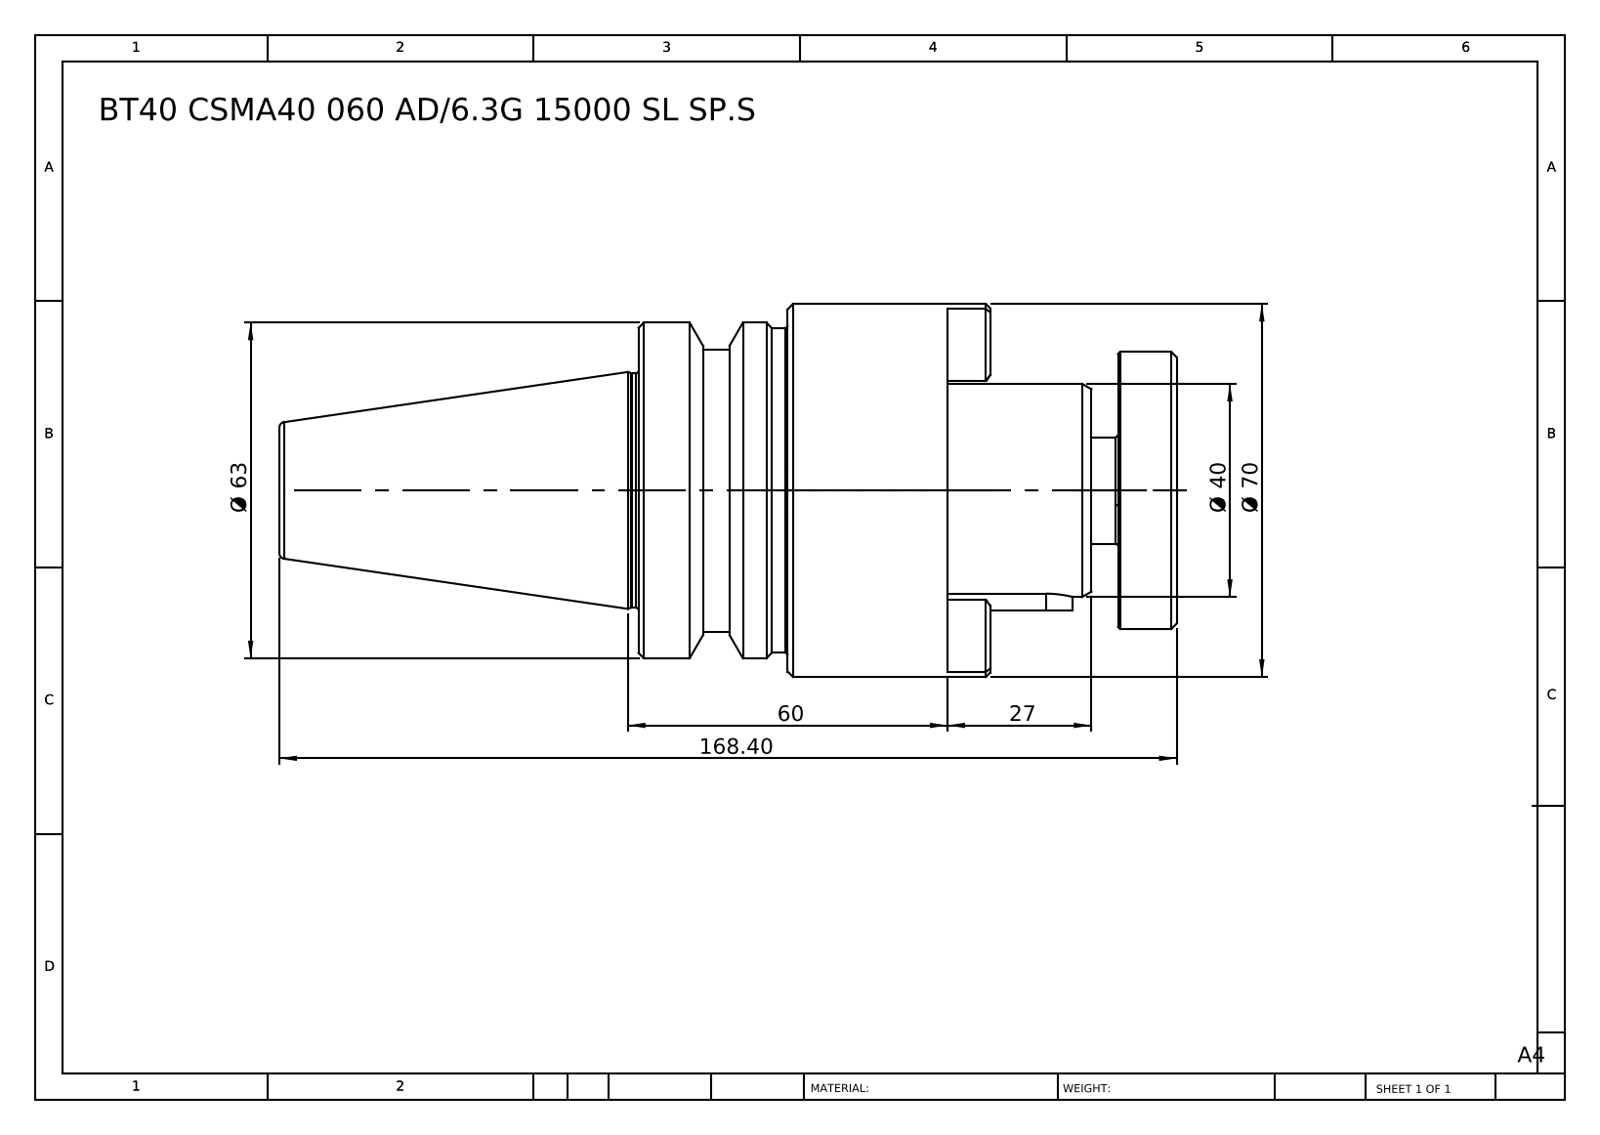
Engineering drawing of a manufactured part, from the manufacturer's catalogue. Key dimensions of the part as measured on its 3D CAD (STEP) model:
Part name (STEP PRODUCT): BT40 CSMA40 060 AD-6.3G 15000 SL SP.S
STEP written by: SolidWorks 2014 (CONFIG_CONTROL_DESIGN)
Units: millimetres
Bodies: 1 solid, 88 faces (23 planar, 23 cylindrical, 42 other)
Overall size (bounding box): 168.4 × 70 × 70
Volume: 325 056 mm³ · Surface area: 36 971 mm²
Round holes (diameter × count): ⌀44 ×1
Round bosses / shafts (diameter × count): ⌀70 ×1, ⌀63 ×1, ⌀61 ×1, ⌀53 ×1, ⌀52 ×1, ⌀40 ×1, ⌀20 ×1
Partial cylindrical surfaces — rounded edges, fillets, slot ends (radius × count): R5 ×1
Main face-to-face distances: 43, 11, 32, 101, 90, 58, 16, 5, 27, 85
